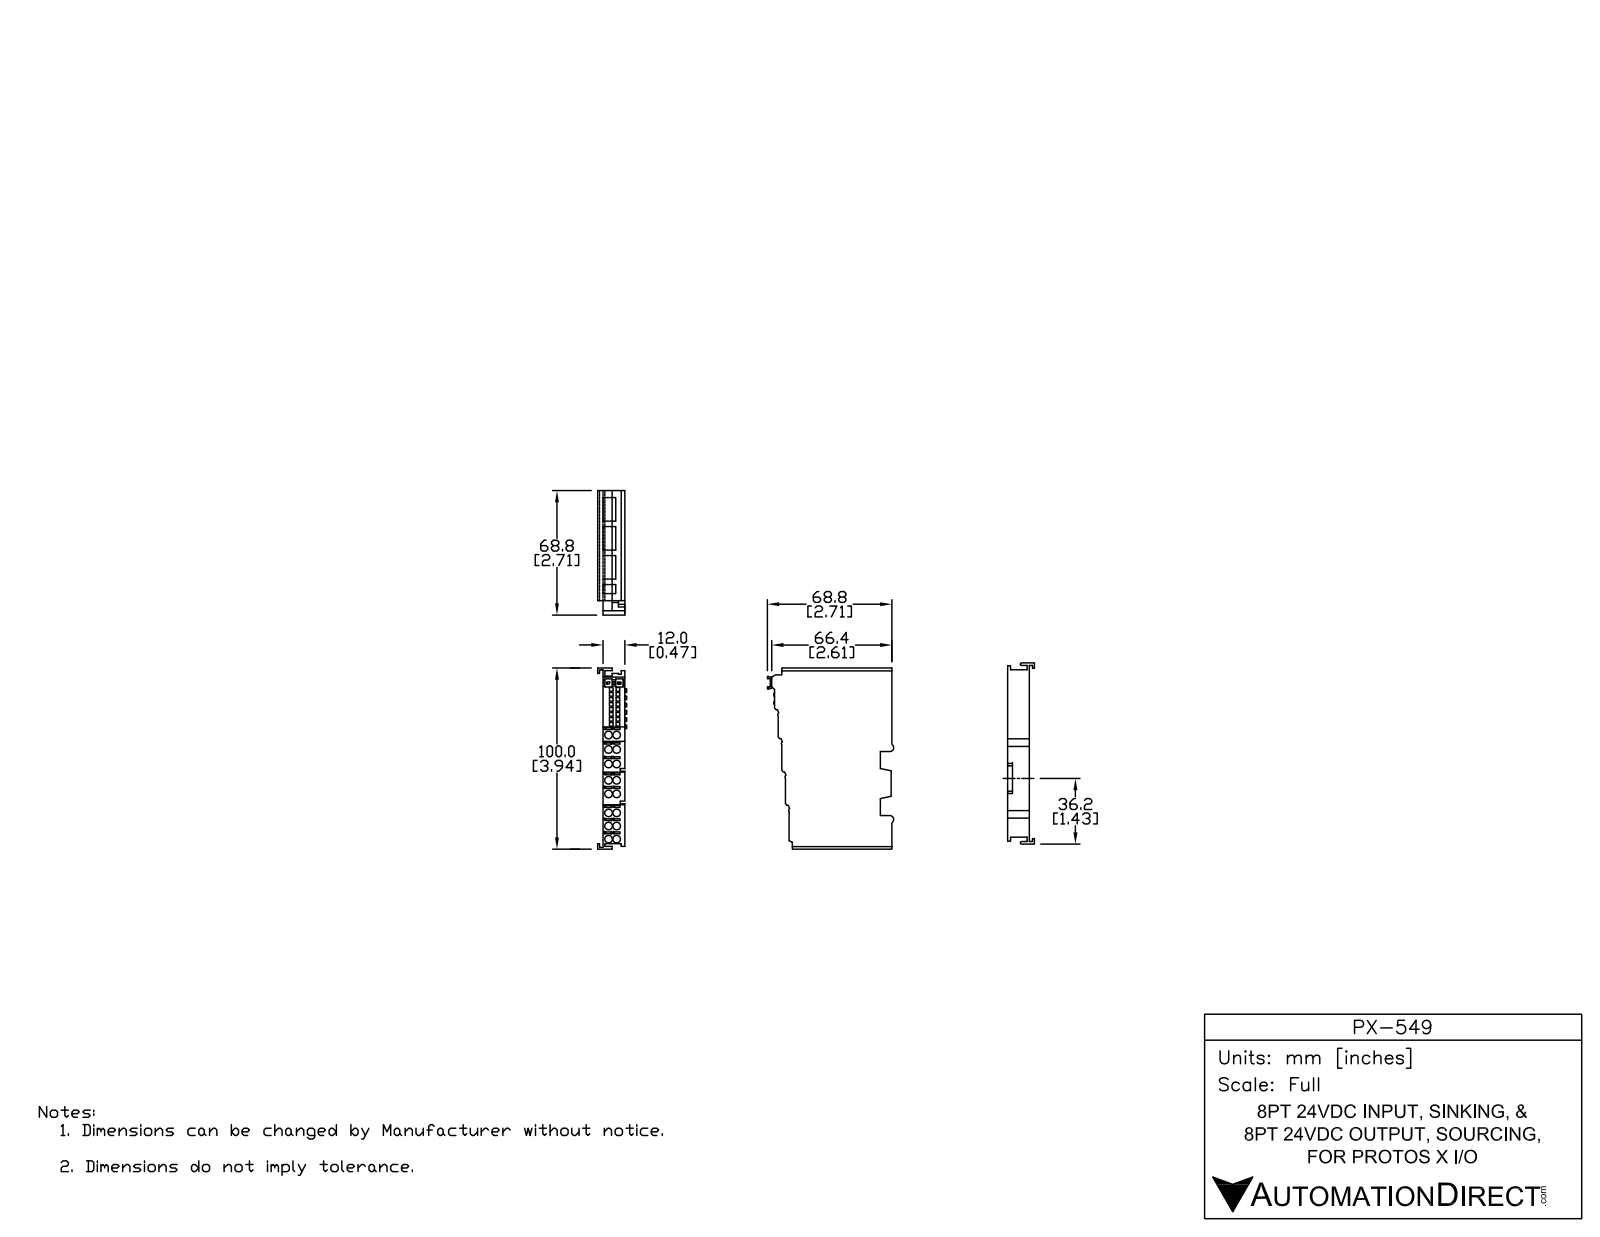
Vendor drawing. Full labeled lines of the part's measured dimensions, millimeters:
Part name (STEP PRODUCT): PX-549
STEP written by: SolidWorks 2014 (AUTOMOTIVE_DESIGN)
Units: millimetres
Bodies: 12 solids, 1152 faces (906 planar, 169 cylindrical, 77 other)
Overall size (bounding box): 100.25 × 70.06 × 15.15
Volume: 60 656 mm³ · Surface area: 28 095 mm²
Round holes (diameter × count): ⌀3.75 ×16
Partial cylindrical surfaces — rounded edges, fillets, slot ends (radius × count): R0.25 ×37, R0.2 ×30, R0.38 ×12, R0.3 ×3, R0.5 ×2, R0.84 ×2, R1.57 ×2, R1.67 ×2
Main face-to-face distances: 12, 1.5, 2.5, 8, 2, 9.75, 8.25, 1, 3, 1.75
Hole centre spacings: 5, 6.75, 8.4, 18, 18.68, 24.75, 25.25, 7
